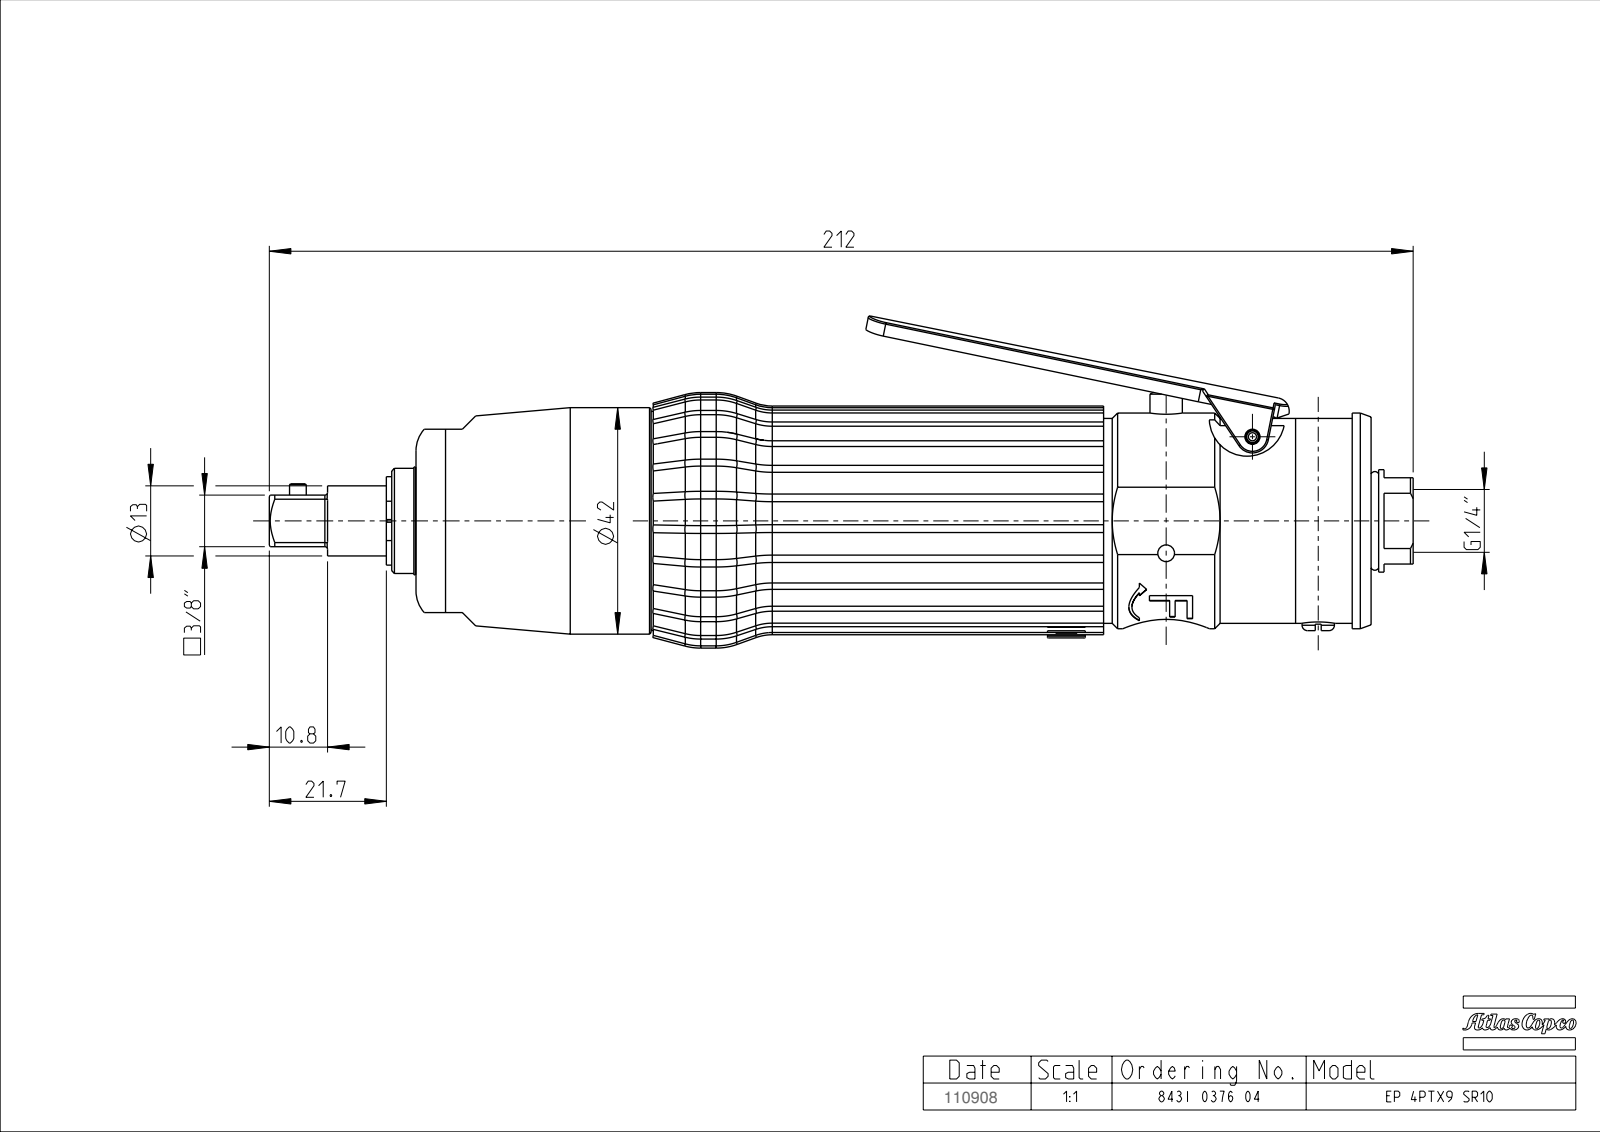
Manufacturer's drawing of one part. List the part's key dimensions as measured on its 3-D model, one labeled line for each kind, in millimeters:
Part name (STEP PRODUCT): EXT_COMP_SW0003
STEP written by: CREO PARAMETRIC BY PTC INC, 2020281 (CONFIG_CONTROL_DESIGN)
Units: millimetres
Bodies: 2 solids, 822 faces (165 planar, 272 cylindrical, 385 other)
Overall size (bounding box): 212 × 60.4 × 47.4
Volume: 238 300 mm³ · Surface area: 35 020 mm²
Round holes (diameter × count): ⌀3.1 ×2, ⌀1.2 ×1, ⌀1.5 ×1, ⌀2 ×1, ⌀2.8 ×1, ⌀4.7 ×1, ⌀5.4 ×1, ⌀6.3 ×1, ⌀11.7 ×1, ⌀15.5 ×1, ⌀19.2 ×1, ⌀19.5 ×1
Round bosses / shafts (diameter × count): ⌀6 ×2, ⌀42 ×1, ⌀40 ×1, ⌀38 ×1, ⌀36.5 ×1, ⌀21 ×1, ⌀20 ×1, ⌀19.2 ×1
Partial cylindrical surfaces — rounded edges, fillets, slot ends (radius × count): R1 ×95, R0.5 ×10, R3.5 ×6, R0.3 ×4, R3 ×2, R4 ×2, R6.2 ×1, R7 ×1
Main face-to-face distances: 1, 177.1, 0.5, 2, 181.6, 38, 3.2, 12.8, 36, 122.6
Hole centre spacings: 1.4, 2.5, 3.9, 26.9, 161.1, 177.7
